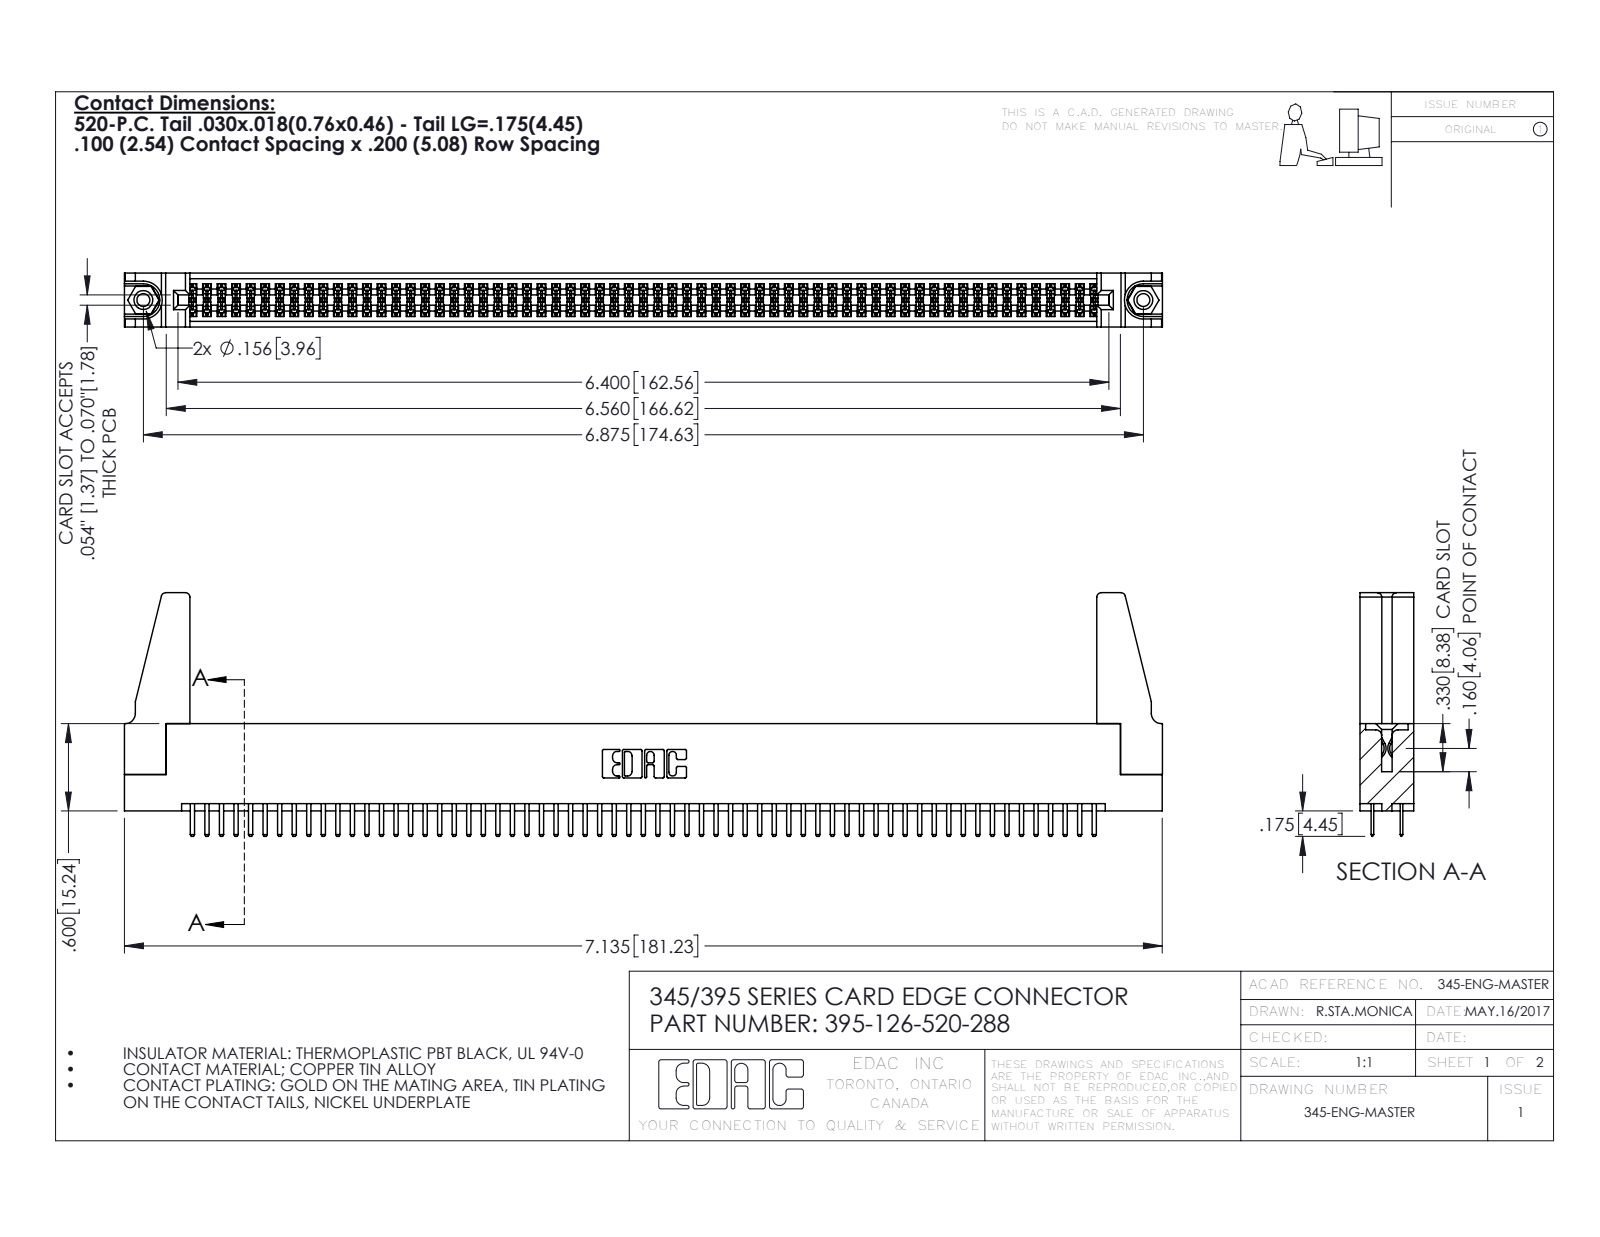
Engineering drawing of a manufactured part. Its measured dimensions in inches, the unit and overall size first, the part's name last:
Units: inches
Overall size (bounding box): 7.136 × 1.675 × 0.37
Round holes (diameter × count): ⌀0.089 ×2, ⌀0.125 ×2, ⌀0.156 ×2, ⌀0.064 ×1
Round bosses / shafts (diameter × count): ⌀0.155 ×2
Partial cylindrical surfaces — rounded edges, fillets, slot ends (radius × count): R0.006 ×189, R0.01 ×130, R0.01 ×22, R0.03 ×8, R0.007 ×6, R0.031 ×6, R0.026 ×3, R0.014 ×2
Main face-to-face distances: 0.072, 0.298, 0.37, 0.2, 0.098, 0.272, 0.025, 0.225, 0.022, 0.072
Hole centre spacings: 0.27, 6.639, 6.875
Volume: 1.281 in³ · Surface area: 45.95 in²
Bodies: 131 solids, 7054 faces (4562 planar, 2476 cylindrical, 16 other)
Part name (STEP PRODUCT): 345-292-001_345-293-120; 345-250-001_345-250-001-102; 345 Part_Flush Mounting Lugs - 0.156 Dia-TH; 395-126-520-288 (+1 more)
STEP written by: SolidWorks 2016 (CONFIG_CONTROL_DESIGN)
